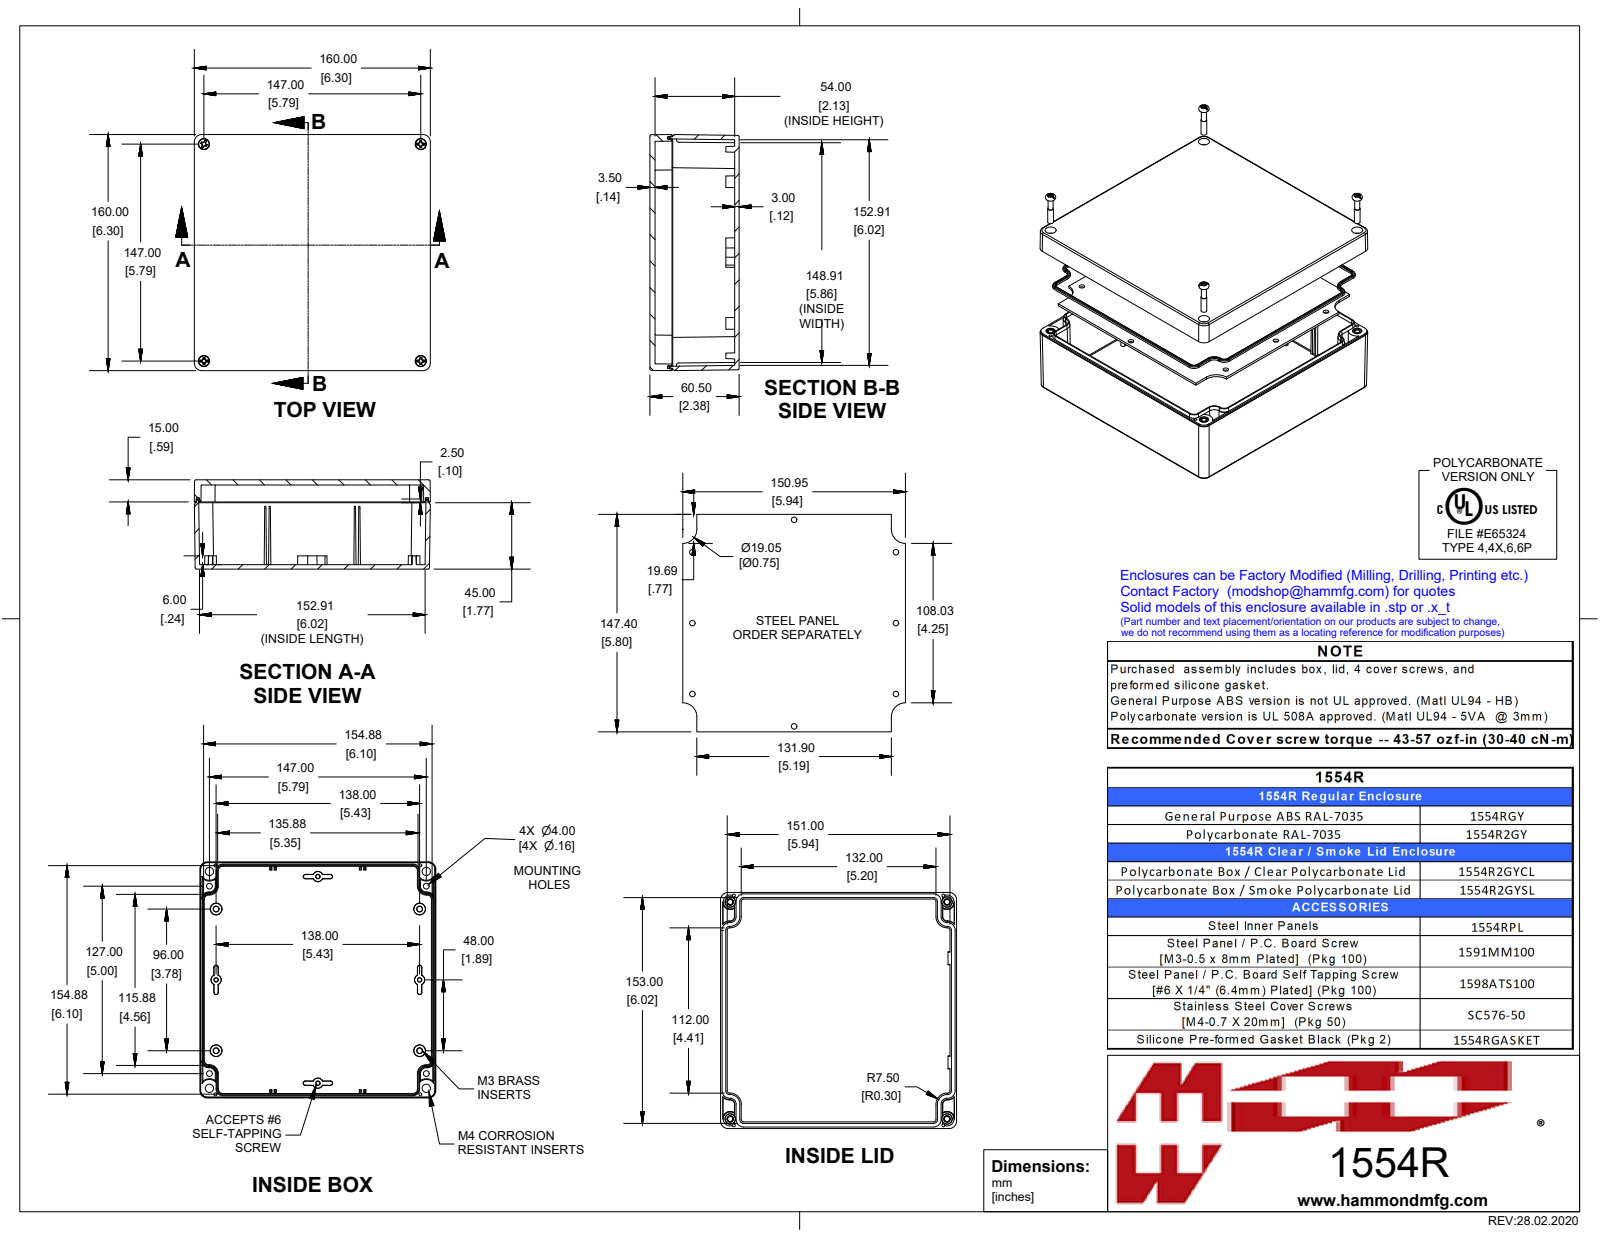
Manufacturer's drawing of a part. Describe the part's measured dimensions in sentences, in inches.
The part is named "1554R2GY". Its 3-D file was written by "SolidWorks 2019 (AUTOMOTIVE_DESIGN)". It is 16 solids with 1384 faces: 392 planar, 352 cylindrical and 640 other. Overall it measures 6.299 by 6.299 by 2.382 inches. Its volume is 19.95 cubic inches and its surface area 378.5 square inches. Round holes: 8 of diameter 0.079, 4 of diameter 0.097, 4 of diameter 0.11, 4 of diameter 0.128, 4 of diameter 0.138, 4 of diameter 0.147, 4 of diameter 0.276. Round bosses or shafts: 4 of diameter 0.25, 4 of diameter 0.218, 4 of diameter 0.21, 4 of diameter 0.19, 4 of diameter 0.154, 4 of diameter 0.153, 4 of diameter 0.15, 4 of diameter 0.135. Partial cylindrical surfaces (rounded edges, fillets, slot ends): 44 of radius 0.02, 8 of radius 0.039, 8 of radius 0.197, 4 of radius 0.187, 4 of radius 0.375, 2 of radius 0.059. The main face-to-face distances are 0.118, 2.382, 0.138, 2.264, 0.354, 0.236, 2.028, 2.244, 2.126, 1.89. The hole center spacings are 5.433, 2.851, 5.635, 5.699, 0.197, 1.019, 1.019, 1.176.
